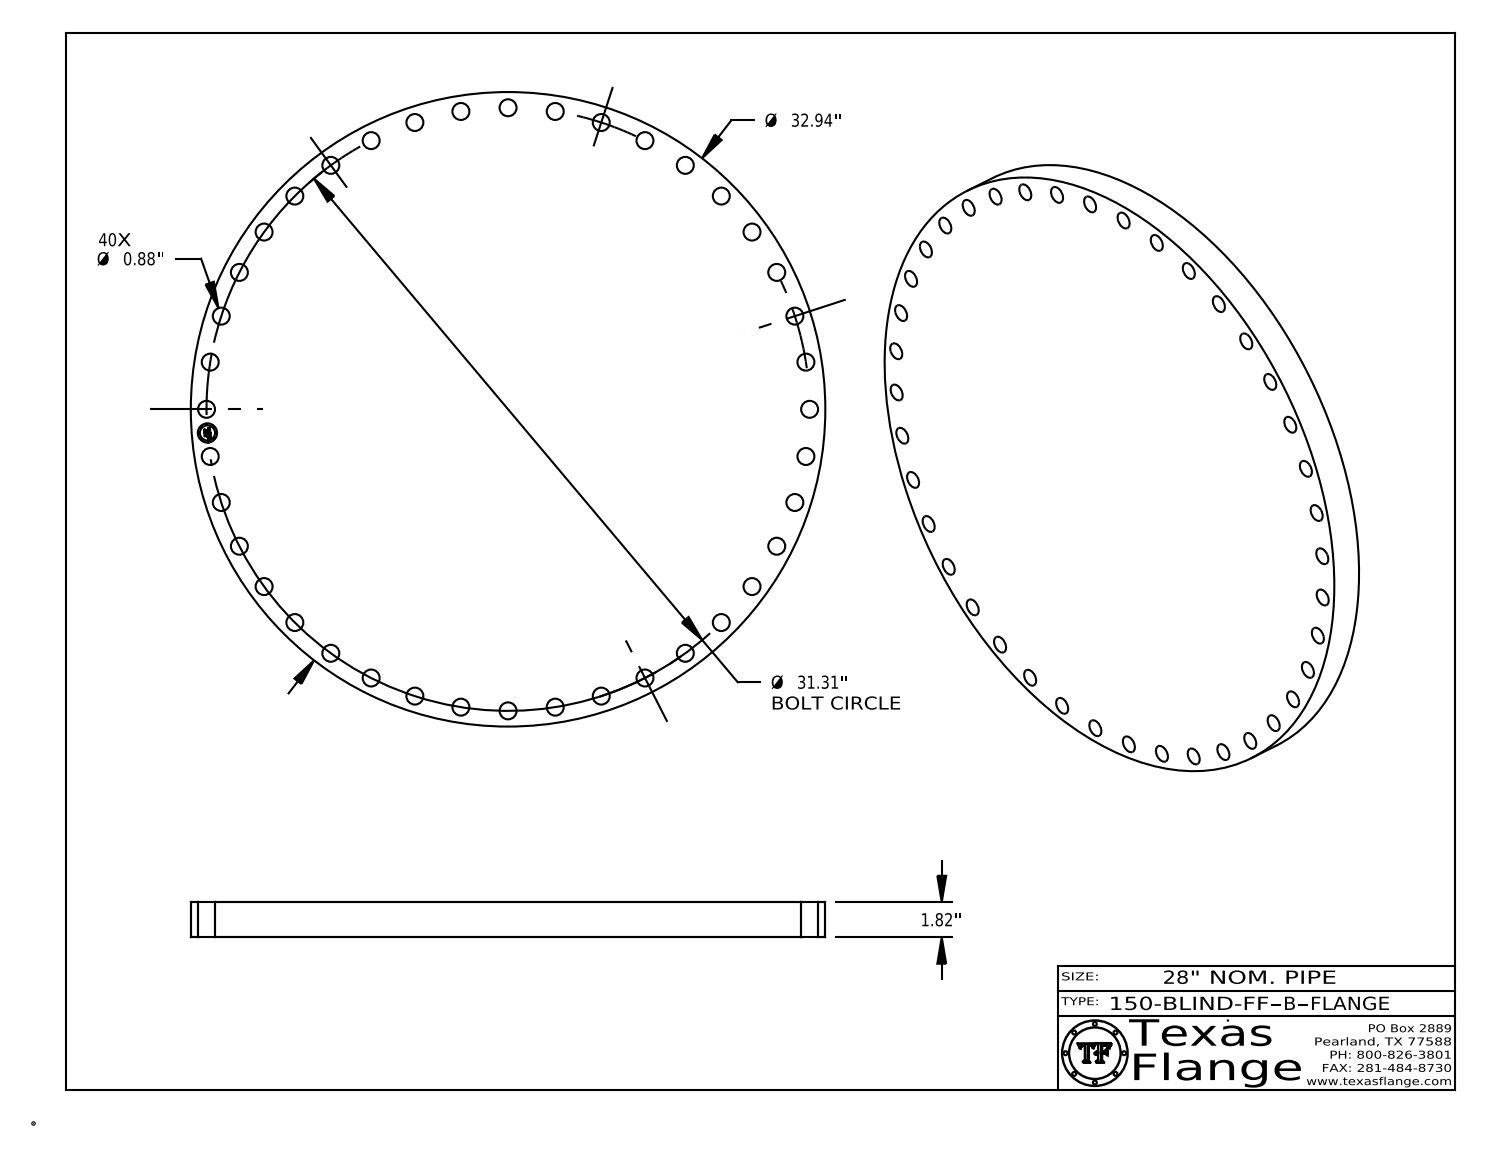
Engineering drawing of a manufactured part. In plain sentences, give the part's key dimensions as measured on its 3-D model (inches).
The part is named "150-BLIND-FF, Series B". Its 3-D file was written by "CATIA V5 STEP AP214 (AUTOMOTIVE_DESIGN)". It is 1 solid with 469 faces: 367 planar, 102 cylindrical and 0 other. Overall it measures 32.94 by 32.94 by 1.82 inches. Its volume is 1 507 cubic inches and its surface area 2 046 square inches. Round holes: 40 of diameter 0.88, 1 of diameter 1. Round bosses or shafts: 8 of diameter 0.061, 1 of diameter 32.94, 1 of diameter 0.788. The main face-to-face distances are 1.82, 0.015, 1.805, 0.298, 0.292, 0.019, 0.054, 0.193, 0.248, 0.044. The hole center spacings are 4.898, 31.214, 11.982, 28.927, 2.457, 16.359, 20.334, 7.309.
